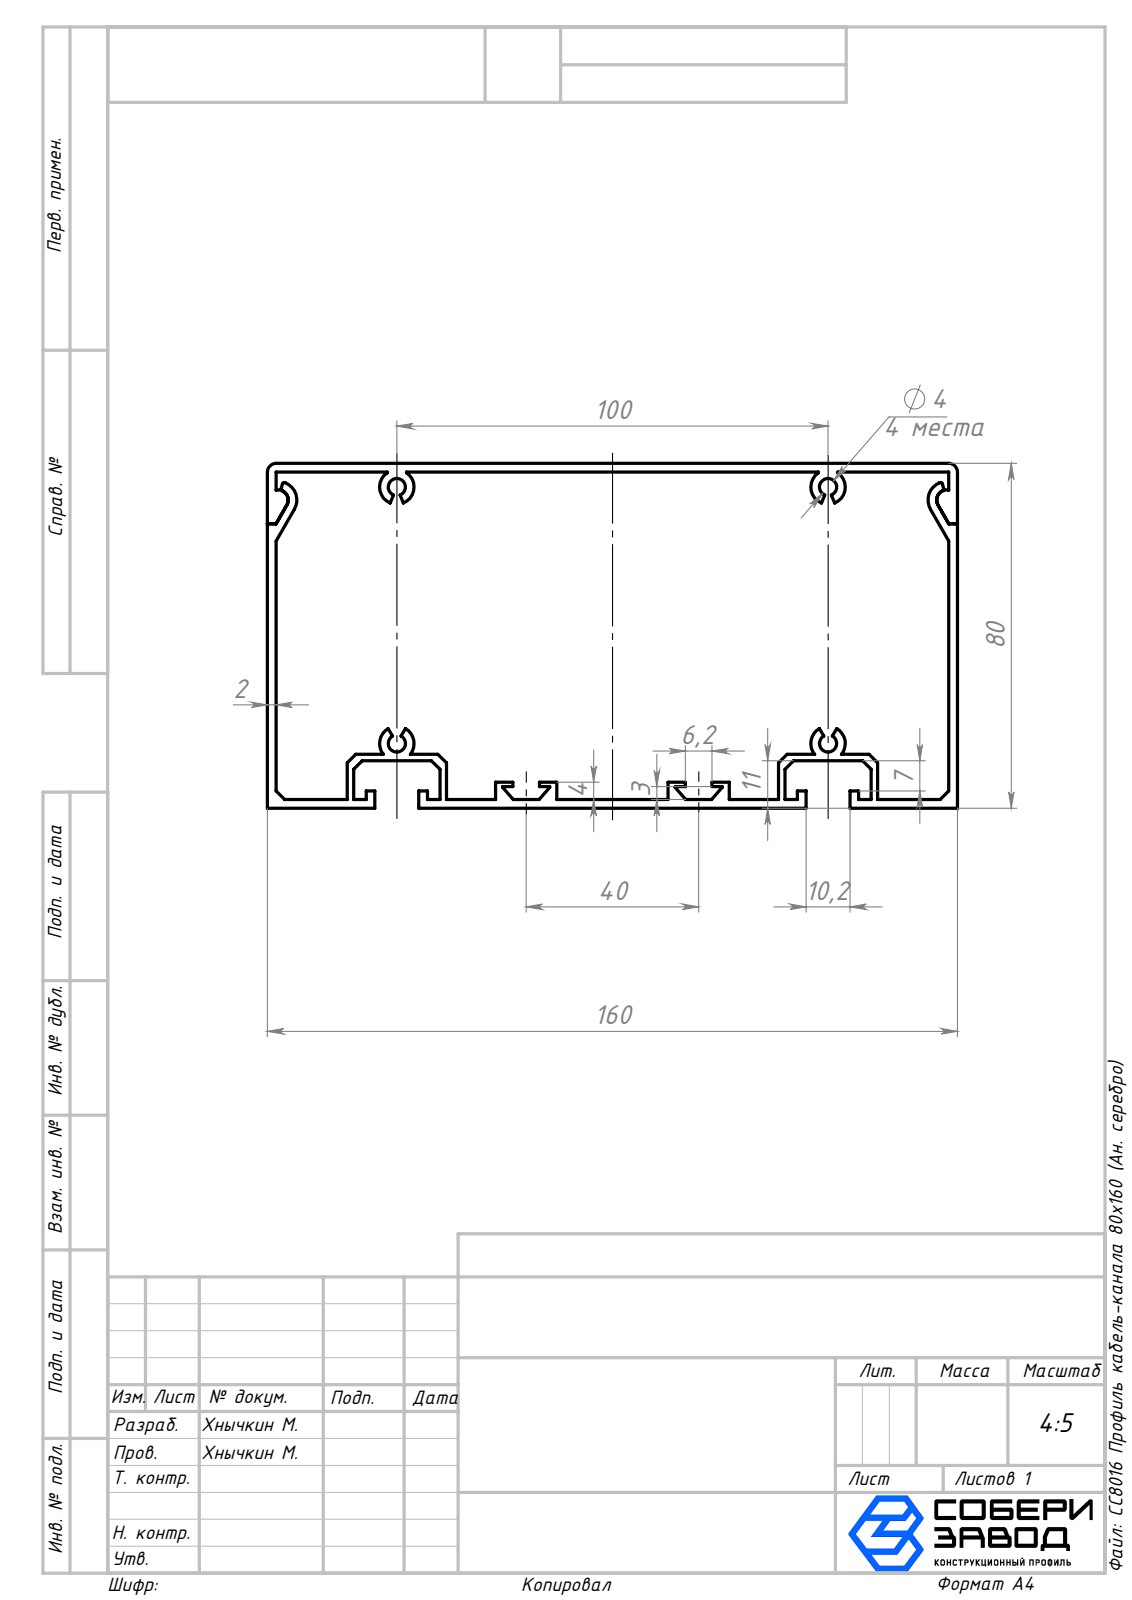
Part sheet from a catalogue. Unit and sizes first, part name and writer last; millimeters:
Units: millimetres
Overall size (bounding box): 160 × 100 × 80
Round holes (diameter × count): ⌀4 ×4
Partial cylindrical surfaces — rounded edges, fillets, slot ends (radius × count): R0.1 ×4, R0.5 ×4, R4 ×4, R2 ×2, R2.35 ×2, R4.35 ×2
Main face-to-face distances: 2, 78, 80, 158, 76, 160, 156, 1.5, 100, 11
Hole centre spacings: 59.5, 100, 116.36
Volume: 128 671 mm³ · Surface area: 130 214 mm²
Bodies: 2 solids, 156 faces (110 planar, 46 cylindrical, 0 other)
Part name (STEP PRODUCT): CC8016 Профиль кабель-канала 80х160 (Ан. серебро); Корпус 80х160_00; Алюм. кабель, крышка 80х160_00
STEP written by: SolidWorks 2026 (AUTOMOTIVE_DESIGN)
